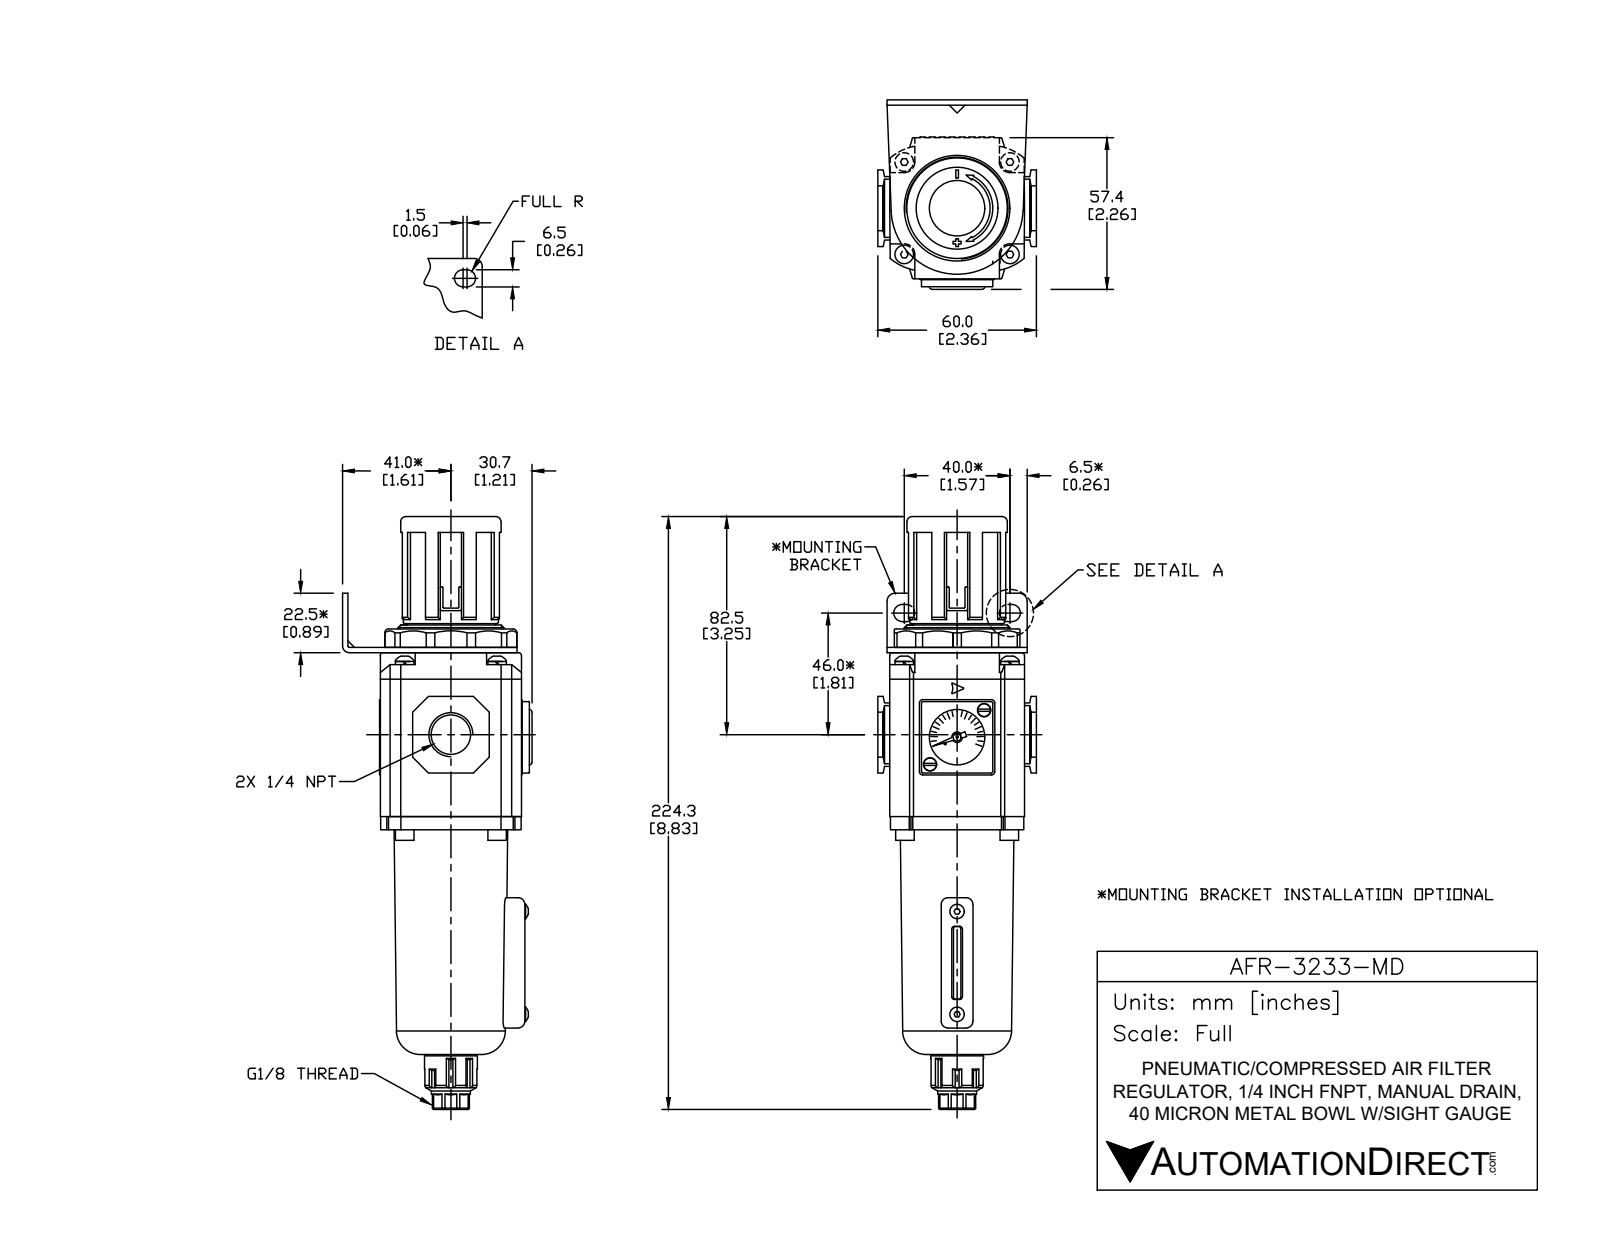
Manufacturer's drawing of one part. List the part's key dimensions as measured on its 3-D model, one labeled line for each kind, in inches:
Part name (STEP PRODUCT): AFR-3233-MD
STEP written by: SolidWorks 2015 (CONFIG_CONTROL_DESIGN)
Units: inches
Bodies: 16 solids, 686 faces (418 planar, 181 cylindrical, 87 other)
Overall size (bounding box): 8.831 × 2.835 × 2.362
Volume: 22.08 in³ · Surface area: 99.8 in²
Round holes (diameter × count): ⌀0.118 ×6, ⌀0.079 ×1, ⌀0.244 ×1, ⌀0.438 ×1, ⌀0.827 ×1, ⌀1.181 ×1, ⌀1.26 ×1
Round bosses / shafts (diameter × count): ⌀0.217 ×6, ⌀0.276 ×4, ⌀0.106 ×2, ⌀1.575 ×1, ⌀1.496 ×1, ⌀1.417 ×1, ⌀1.319 ×1, ⌀0.806 ×1
Partial cylindrical surfaces — rounded edges, fillets, slot ends (radius × count): R0.039 ×16, R0.047 ×10, R0.051 ×8, R0.098 ×8, R0.374 ×8, R0.783 ×8, R0.02 ×6, R0.128 ×6
Main face-to-face distances: 0.079, 2.441, 2.52, 2.102, 2.008, 0.039, 2.185, 2.063, 0.177, 2.638
Hole centre spacings: 1.046, 0.571, 1.378, 1.575, 2.093, 1.141
